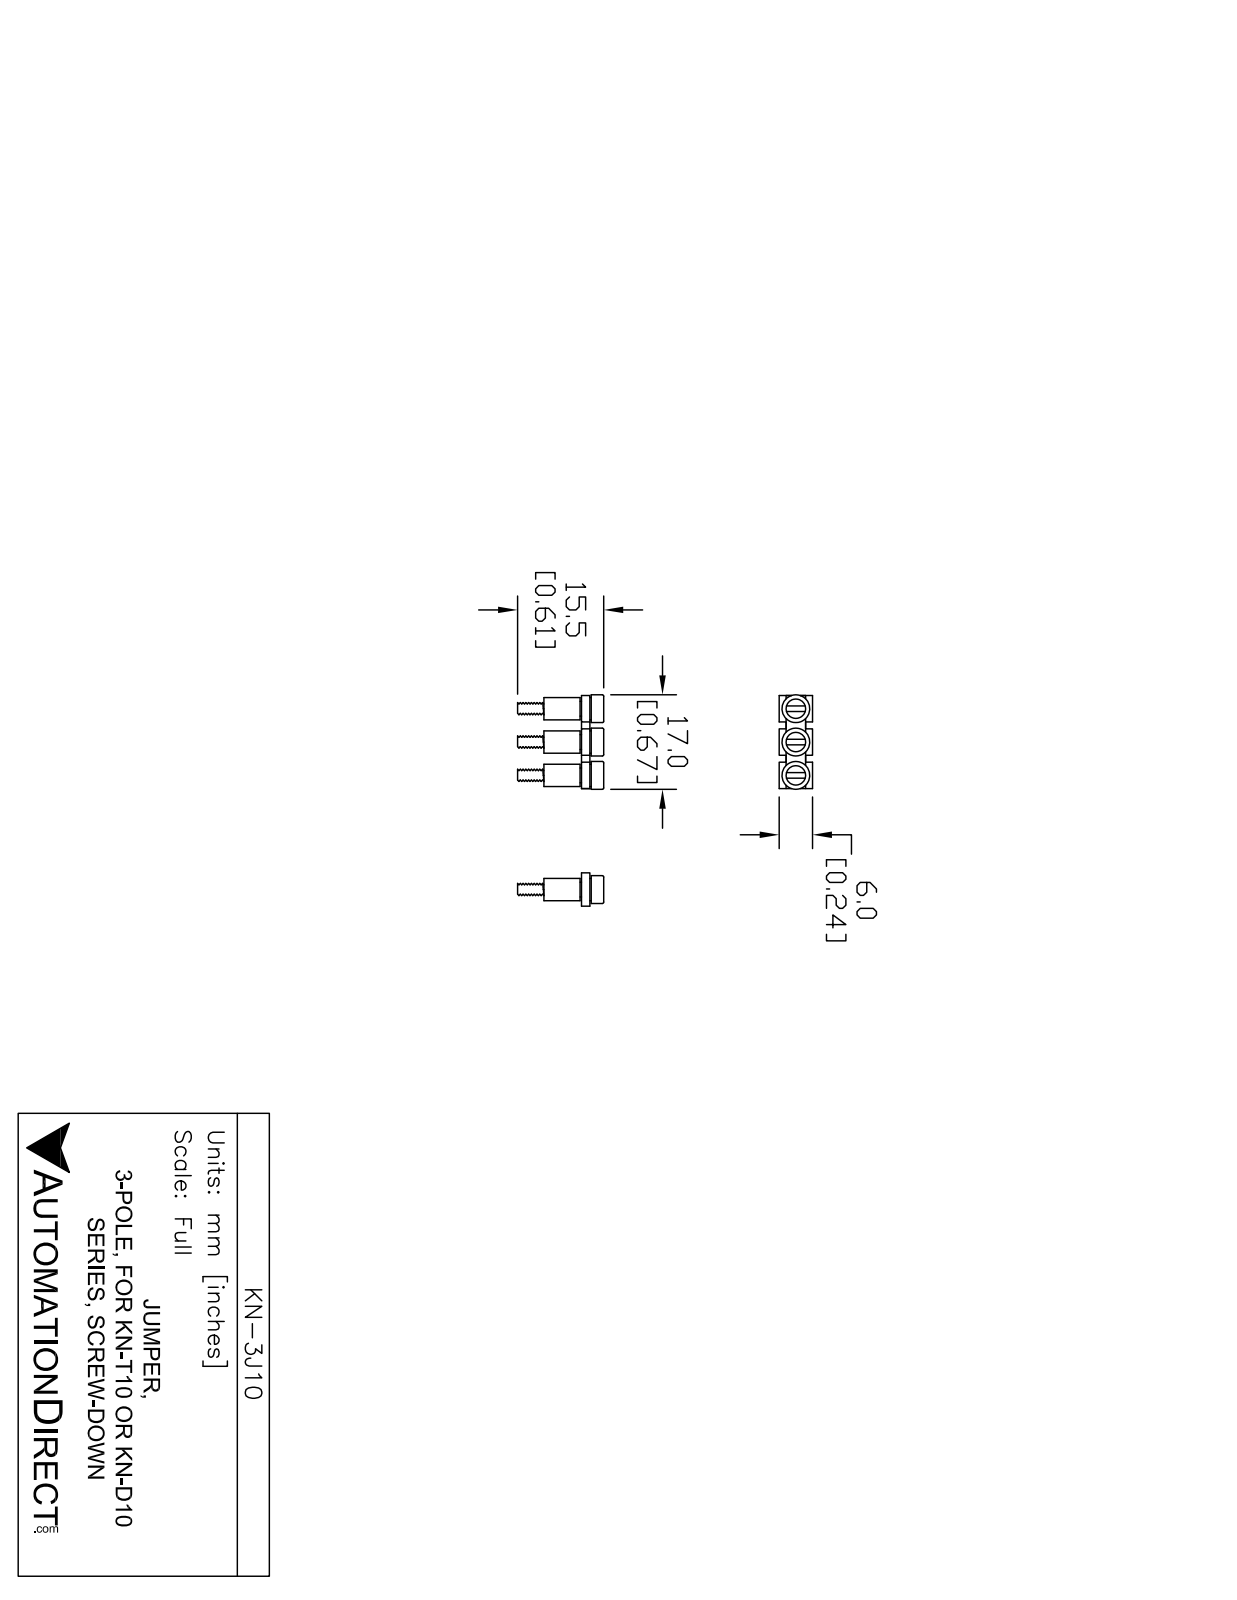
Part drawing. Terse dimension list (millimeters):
name: KN-3J10
written by: SolidWorks 2014 (AUTOMOTIVE_DESIGN)
unit: mm
bodies: 10 solids, 124 faces (61 planar, 45 cylindrical, 18 other)
size: 17 × 15.5 × 6
volume: 543 mm³; area: 1 488 mm²
holes: 3× ⌀3, 3× ⌀3.15, 3× ⌀3.5
bosses: 3× ⌀5, 3× ⌀4, 3× ⌀2.65
face distances: 1.5, 1.75, 6, 2, 1, 4.75, 2.5, 3.5, 10.75, 0.5
hole spacings: 6, 12
